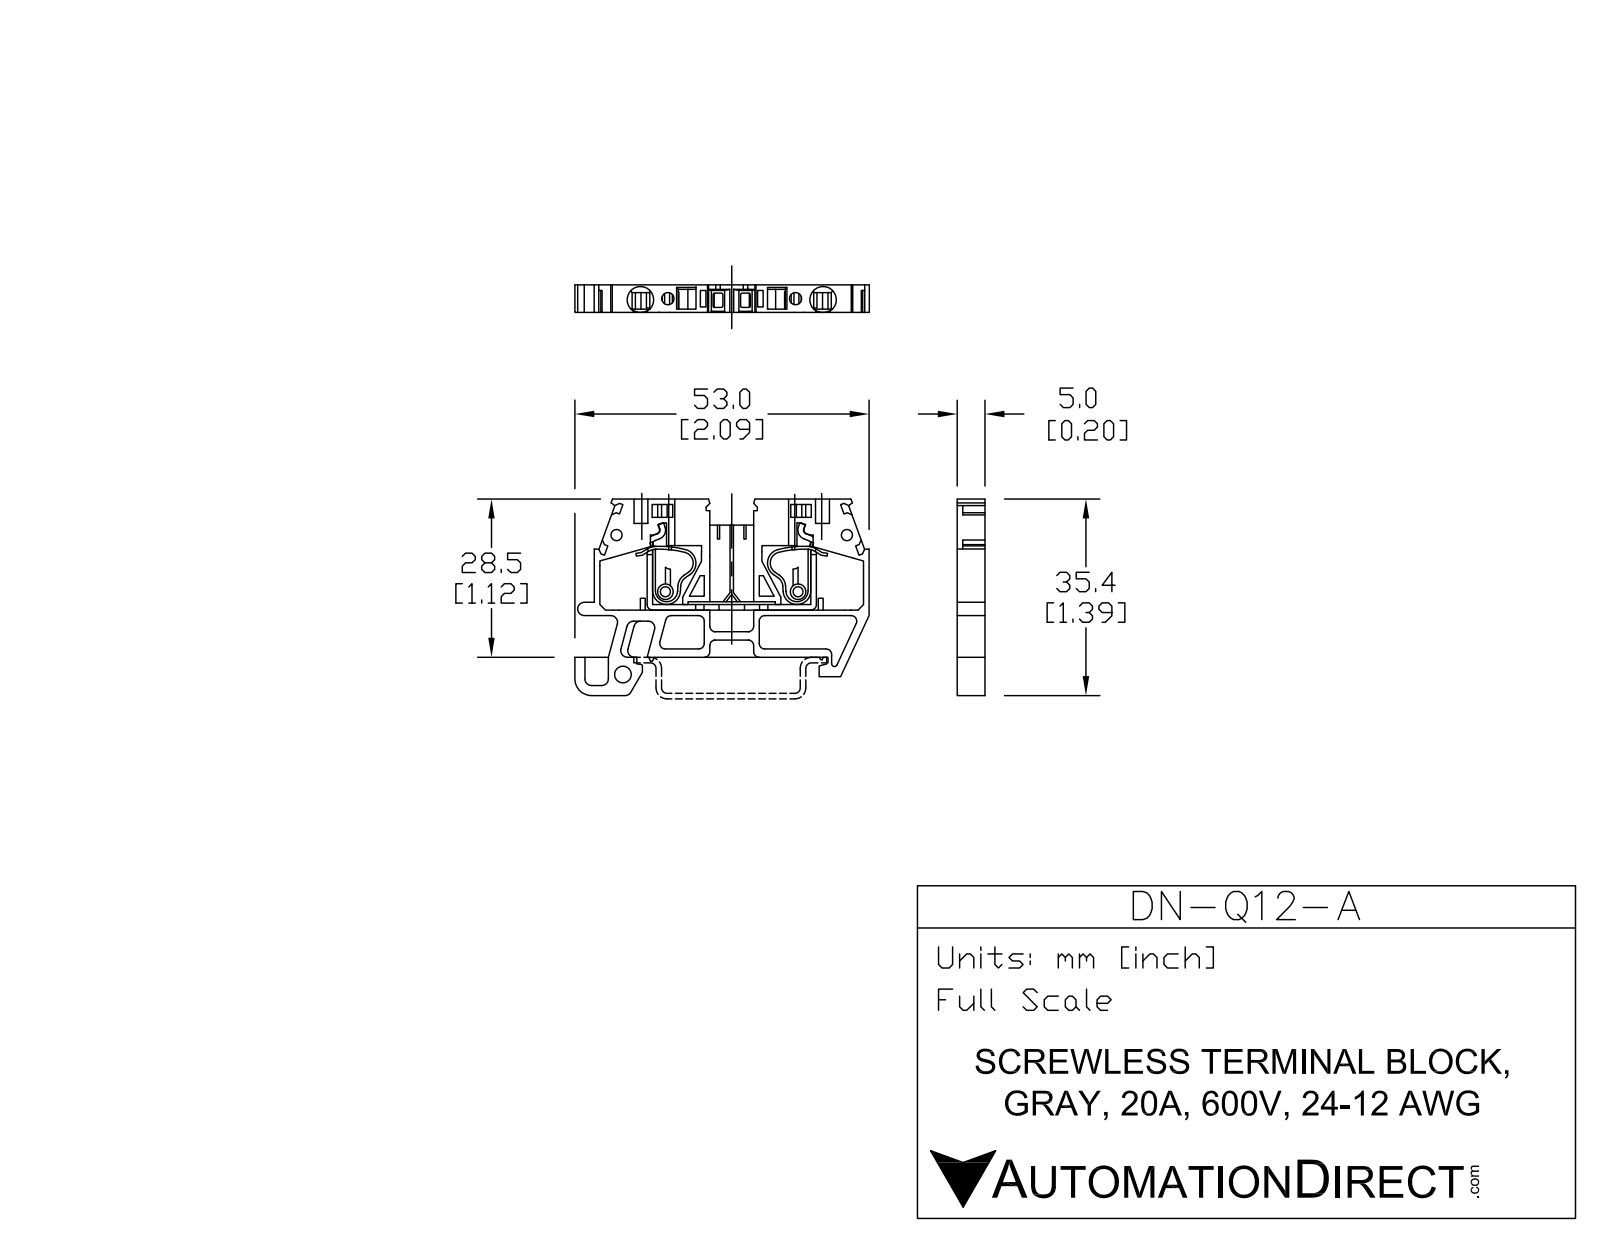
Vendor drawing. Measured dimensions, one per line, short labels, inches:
name: 42416_DN-Q12-A
written by: SolidWorks 2013 (AUTOMOTIVE_DESIGN)
unit: in
bodies: 1 solid, 335 faces (271 planar, 52 cylindrical, 12 other)
size: 2.106 × 1.394 × 0.197
volume: 0.285 in³; area: 8.333 in²
holes: 2× ⌀0.087, 2× ⌀0.102, 2× ⌀0.189, 1× ⌀0.118
rounds: 14× R0.039, 10× R0.047, 1× R0.012, 1× R0.02, 1× R0.118
face distances: 0.197, 0.079, 0.039, 0.193, 0.118, 0.028, 0.114, 0.031, 0.075, 0.165
hole spacings: 0.197, 1.11, 0.913, 0.989, 1.307, 1.654, 1.888
